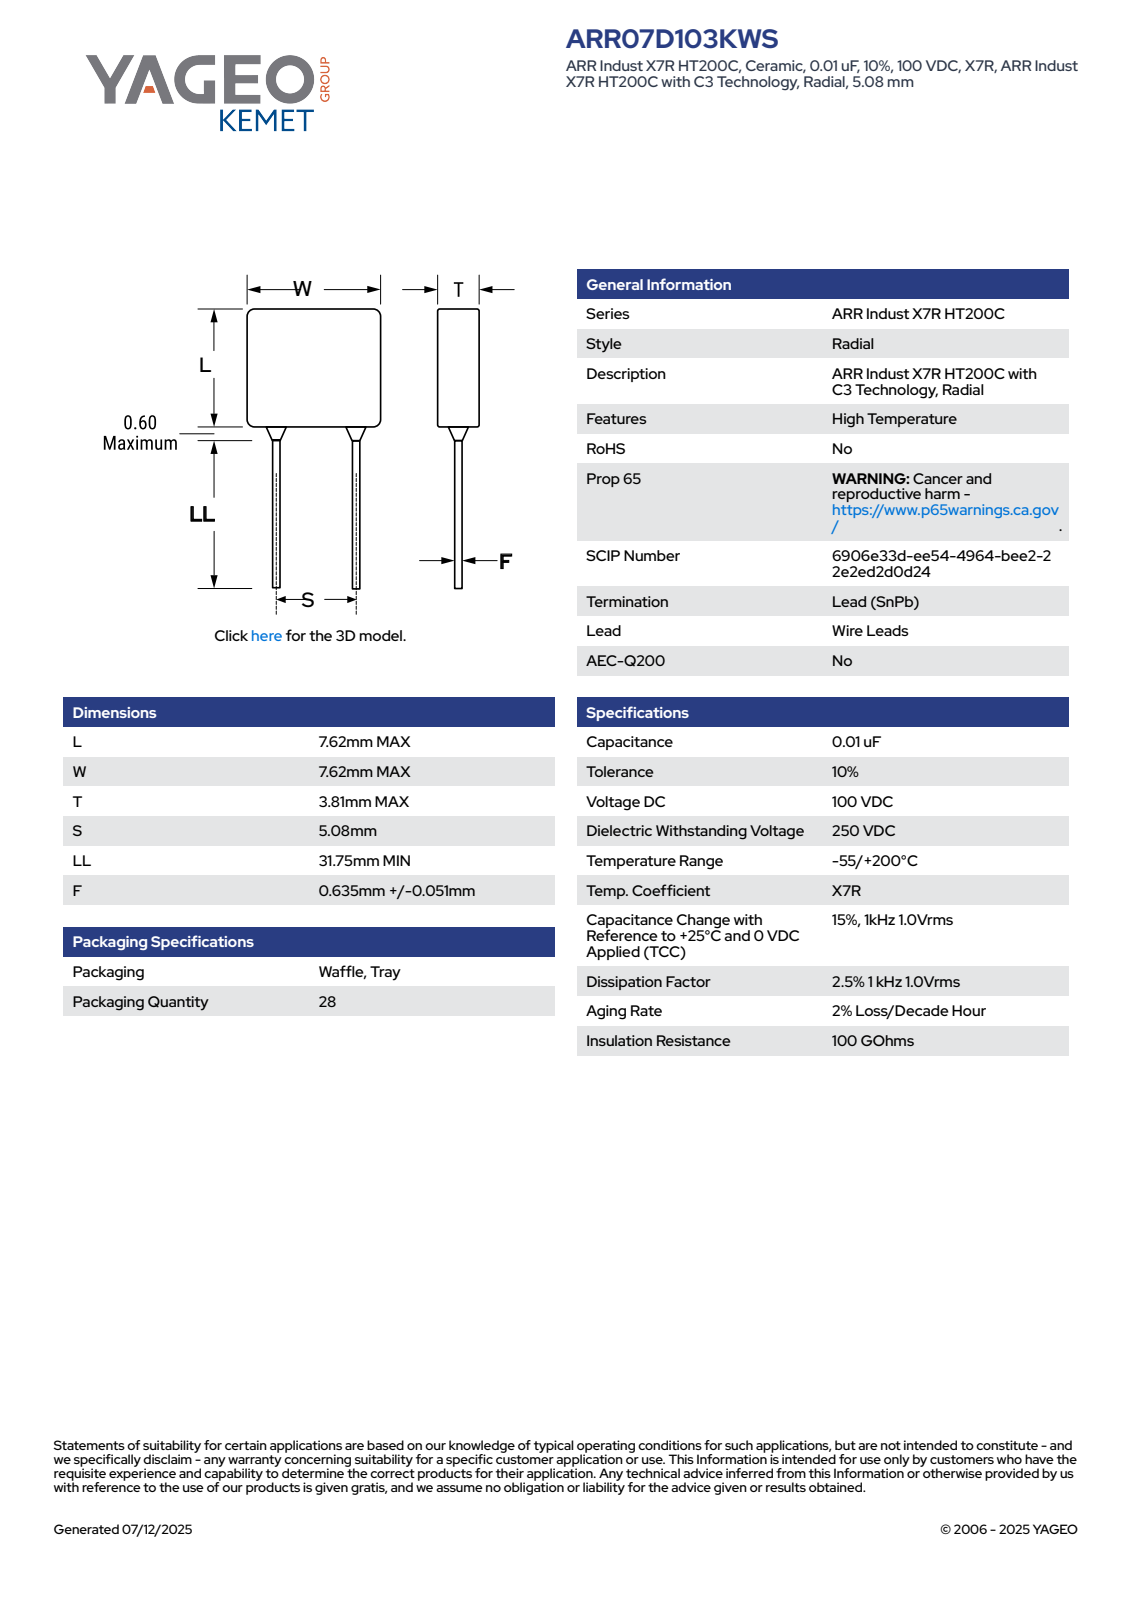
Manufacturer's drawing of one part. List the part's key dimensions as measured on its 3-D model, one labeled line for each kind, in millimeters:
Part name (STEP PRODUCT): CCR_C3_7_L7.62T3.81S5.842LL31.75F0.686W7.62
STEP written by: SolidWorks 2021 (AUTOMOTIVE_DESIGN)
Units: millimetres
Bodies: 4 solids, 77 faces (65 planar, 8 cylindrical, 4 other)
Overall size (bounding box): 39.97 × 7.62 × 3.81
Volume: 245 mm³ · Surface area: 378 mm²
Round bosses / shafts (diameter × count): ⌀0.69 ×2
Partial cylindrical surfaces — rounded edges, fillets, slot ends (radius × count): R0.5 ×4
Main face-to-face distances: 3.81, 7.62, 3.76, 32.35, 39.97, 36.86, 4.51, 3.11, 35.65, 3.3
